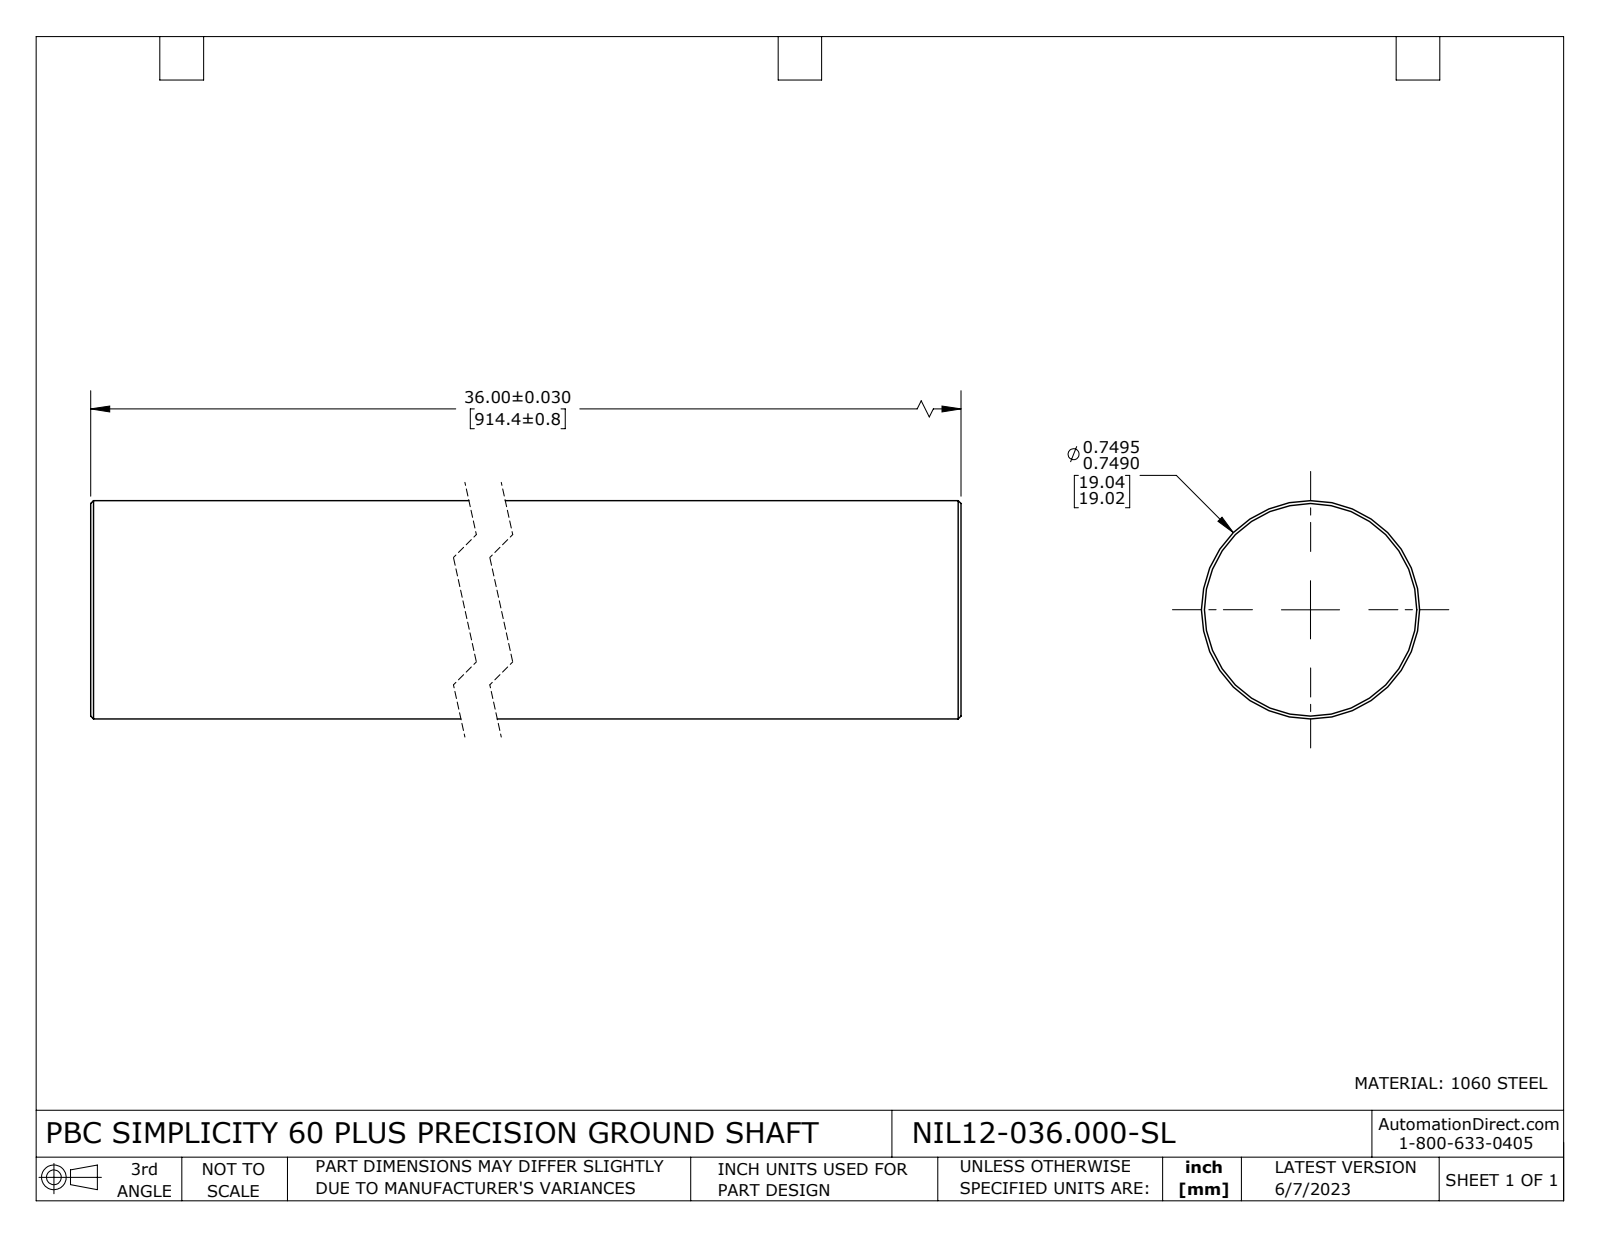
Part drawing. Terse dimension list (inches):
name: NIL12-036.000-SL
written by: SolidWorks 2021 (CONFIG_CONTROL_DESIGN)
unit: in
bodies: 1 solid, 8 faces (2 planar, 2 cylindrical, 4 other)
size: 36 × 0.75 × 0.75
volume: 15.9 in³; area: 85.68 in²
bosses: 1× ⌀0.75
face distances: 36
